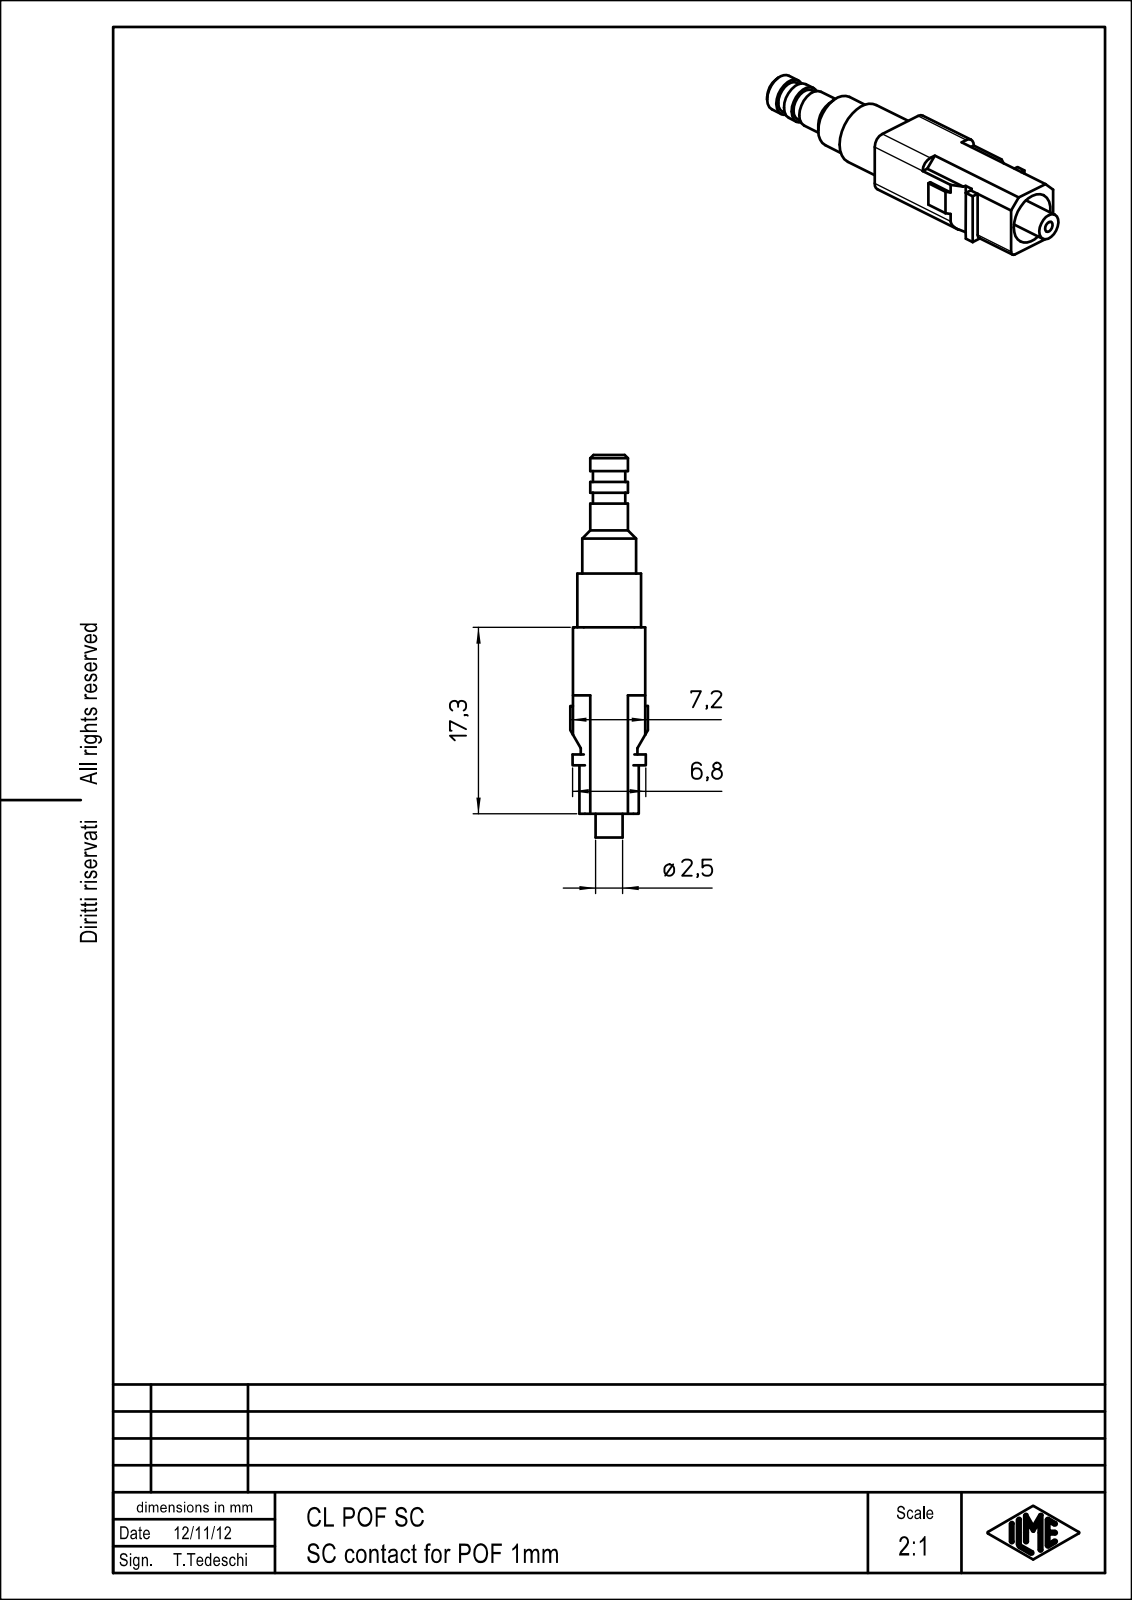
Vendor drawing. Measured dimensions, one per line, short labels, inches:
name: tappo; CONTATTO_SC; CL_POF_SC
written by: Creo Elements/Direct Modeling 18.0B 02-Dec-2011 (C) Parametric Technology GmbH (AUTOMOTIVE_DESIGN)
unit: in
bodies: 2 solids, 92 faces (48 planar, 34 cylindrical, 10 other)
size: 2.1 × 0.283 × 0.232
volume: 0.059 in³; area: 1.962 in²
holes: 1× ⌀0.039, 1× ⌀0.091, 1× ⌀0.102, 1× ⌀0.128, 1× ⌀0.189
bosses: 1× ⌀0.232, 1× ⌀0.197, 1× ⌀0.181, 1× ⌀0.138, 1× ⌀0.118, 1× ⌀0.098
rounds: 4× R0.039, 2× R0.02
face distances: 0.232, 0.026, 0.207, 0.024, 0.24, 0.264, 0.181, 0.217, 0.039, 1.004
